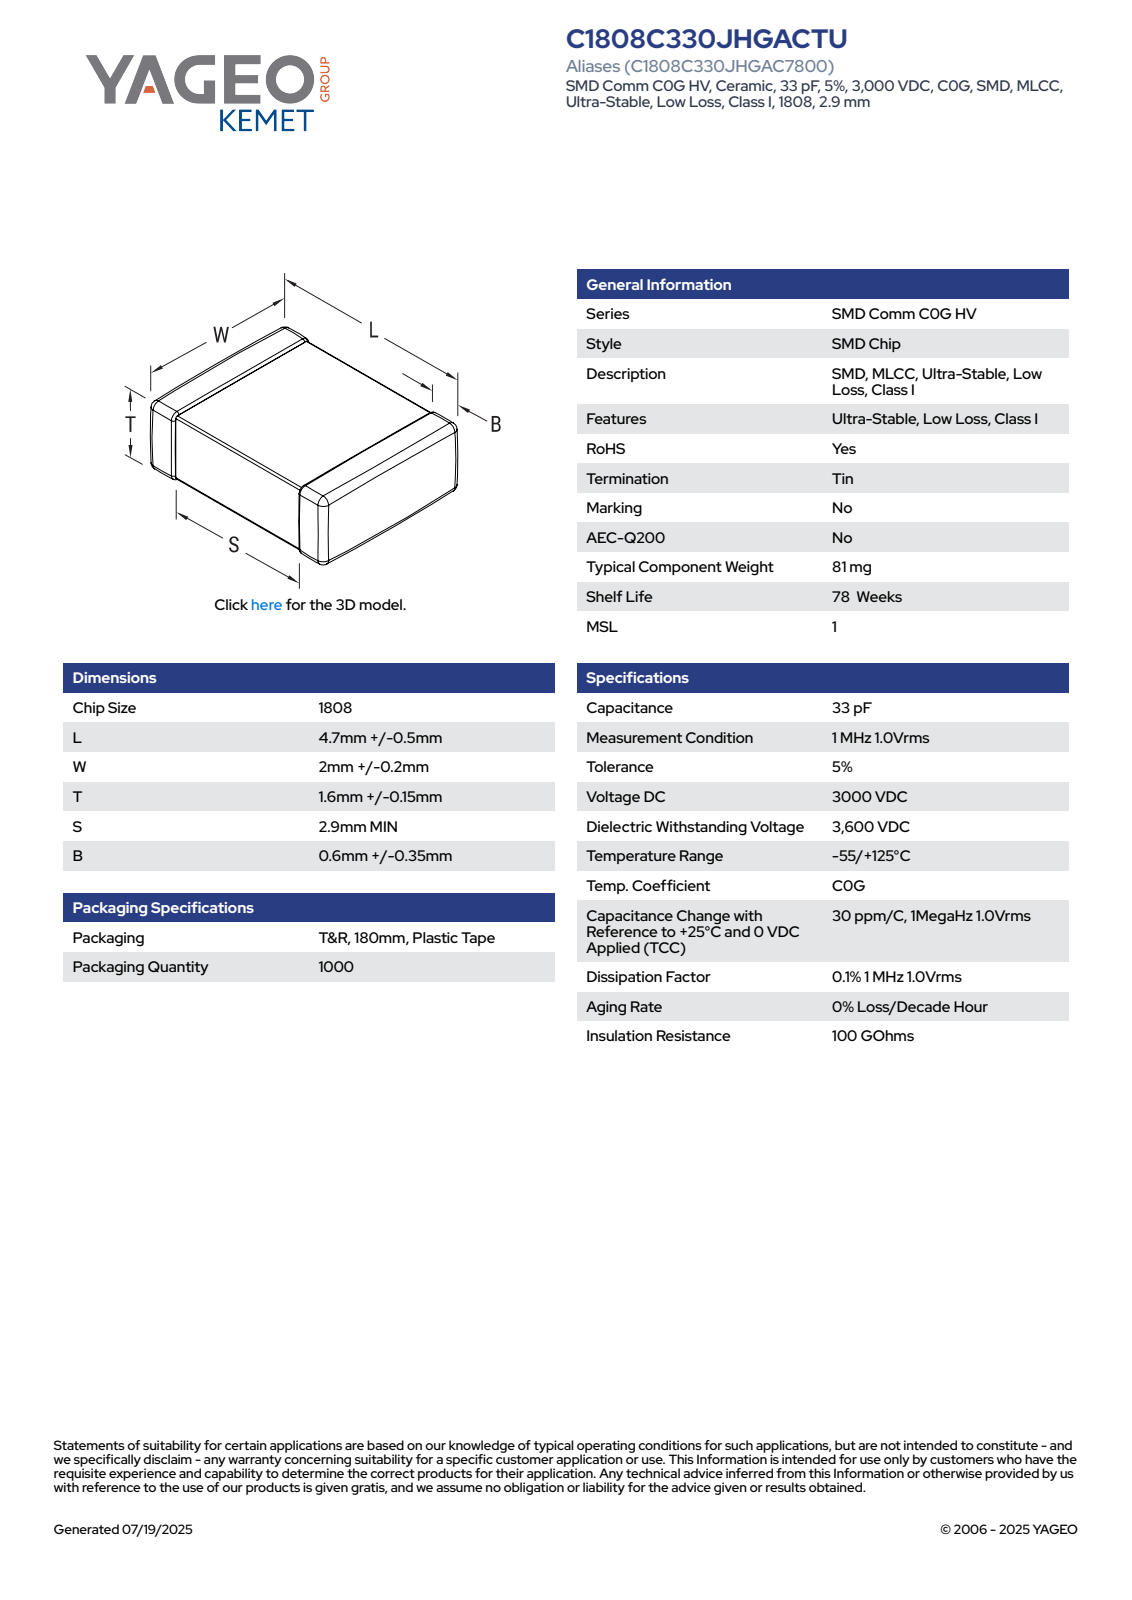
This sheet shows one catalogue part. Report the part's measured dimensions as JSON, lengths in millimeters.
{"part_name": "CCS_CCSTDNOS_1808_L5.2W2.2T1.75B0.95", "step_written_by": "SolidWorks 2014 (AUTOMOTIVE_DESIGN)", "units": "millimeters", "bodies": {"solids": 4, "faces": 125, "planar": 71, "cylindrical": 38, "other": 16}, "overall_size": [5.2, 2.2, 1.75], "volume_mm3": 19, "surface_area_mm2": 48, "face_to_face_distances": [1.7, 1.65, 2.15, 2.1, 1.75, 5.2, 2.2, 1.71, 1.66, 0.89]}
